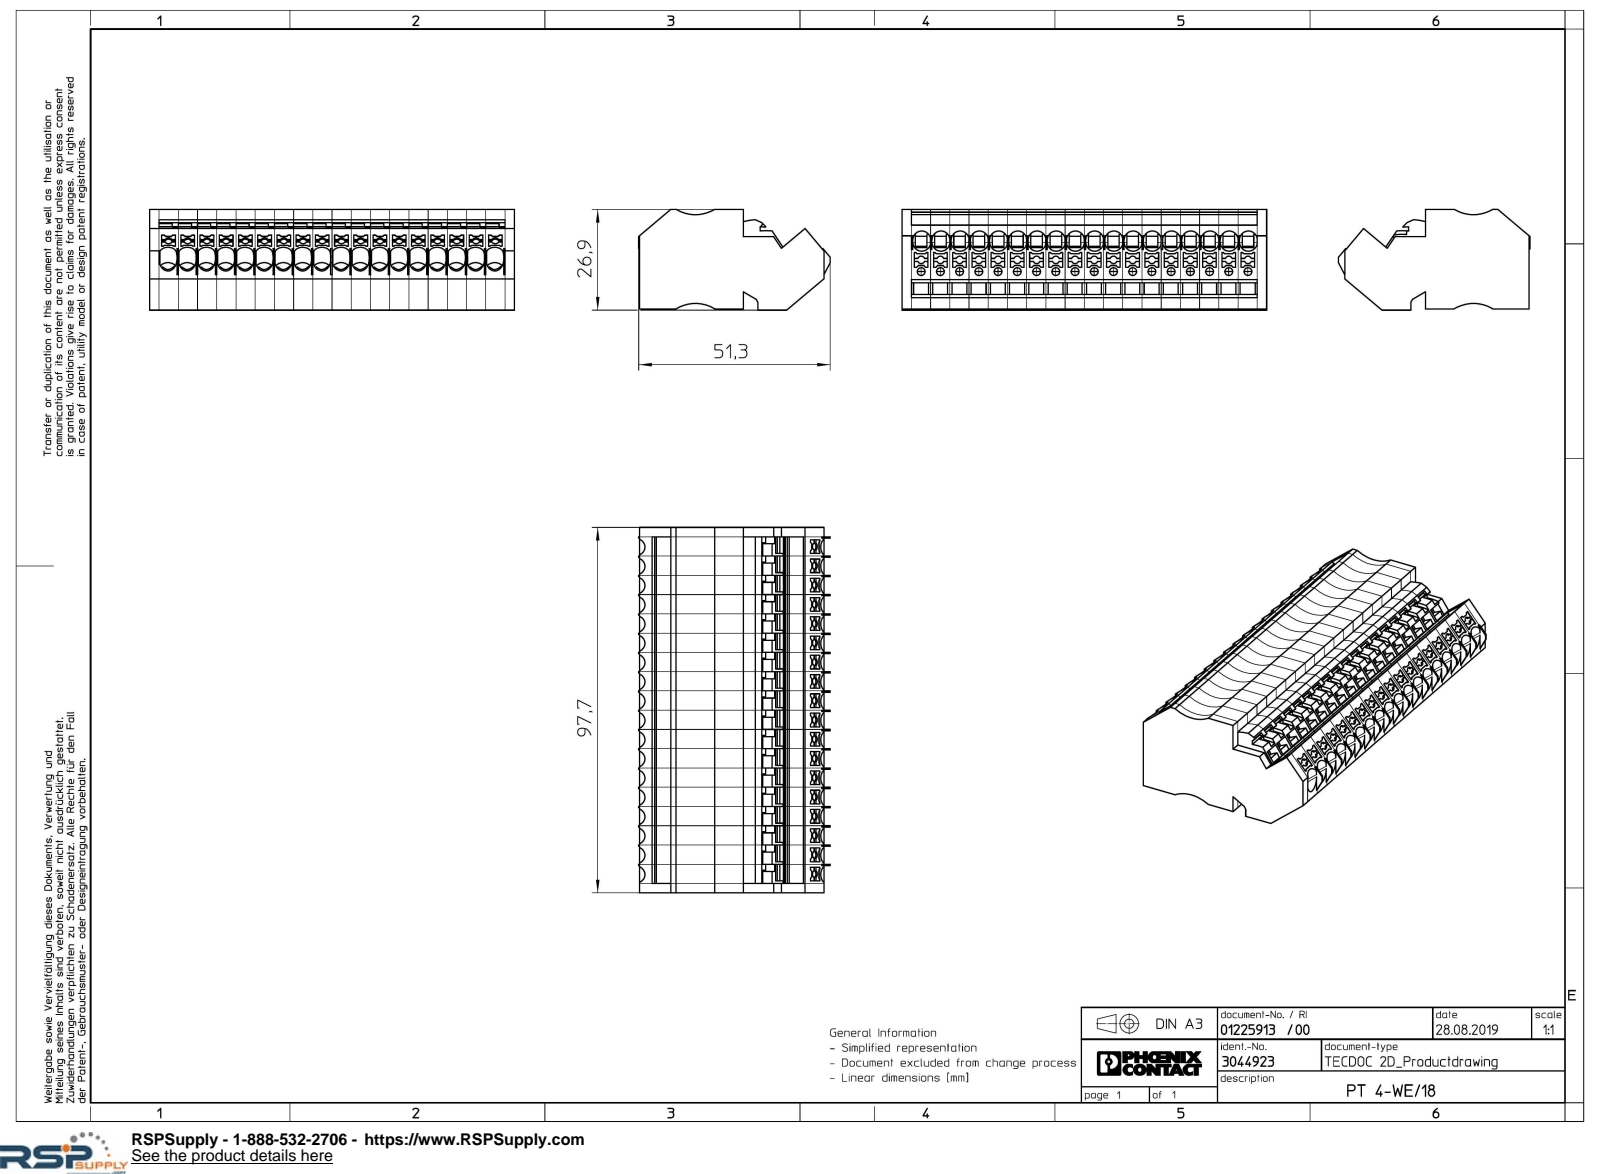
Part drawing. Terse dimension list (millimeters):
name: PT_4_WE_18-select
written by: Creo Elements/Direct Modeling 20.1A 29-Sep-2018 (C) Parametric Technology GmbH (AUTOMOTIVE_DESIGN)
unit: mm
bodies: 1 solid, 3003 faces (2603 planar, 364 cylindrical, 36 other)
size: 97.7 × 51.3 × 26.9
volume: 87 835 mm³; area: 33 721 mm²
holes: 18× ⌀2.1
rounds: 72× R2.4, 36× R1, 3× R1.03, 2× R10, 1× R1.05, 1× R1.78, 1× R12.4, 1× R13.38
face distances: 3.15, 3.85, 7, 97.7, 19.6, 26.6, 22.75, 5.15, 15.45, 10.3
hole spacings: 5.15, 10.3, 15.45, 20.6, 25.75, 30.9, 36.05, 41.2
